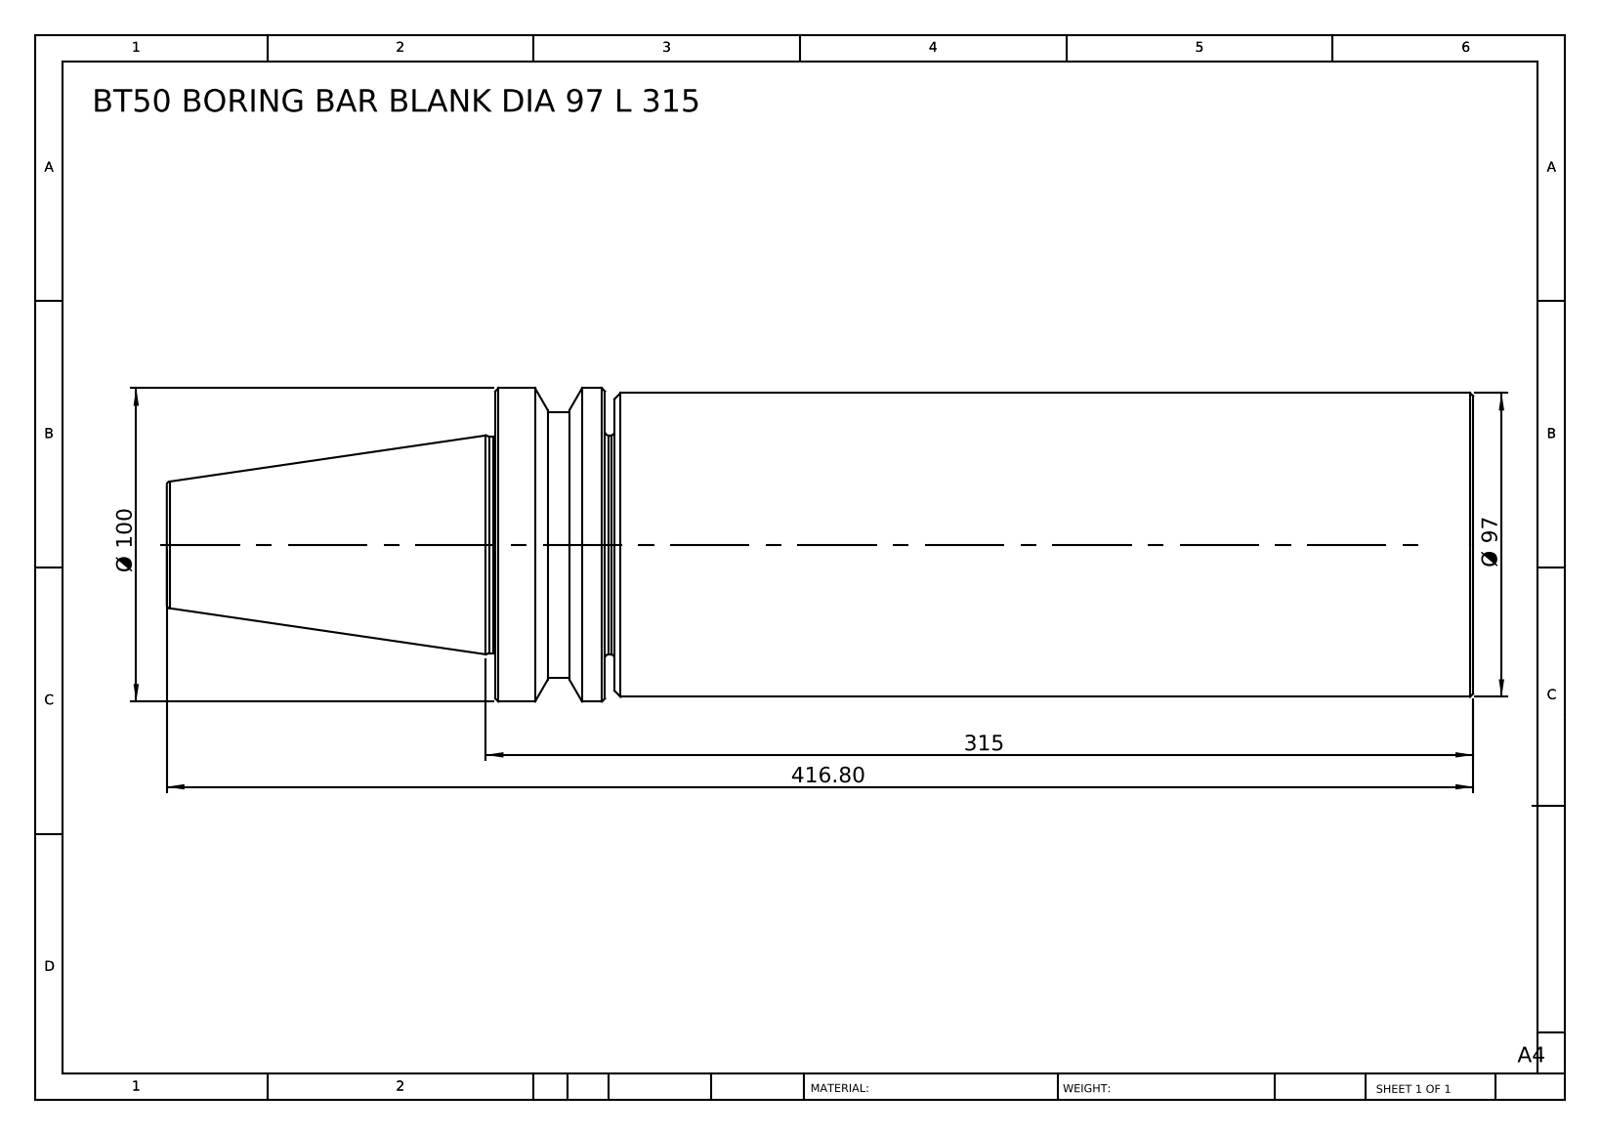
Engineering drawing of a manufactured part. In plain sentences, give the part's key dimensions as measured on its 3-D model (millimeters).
The part is named "BT50 BORING BAR BLANK DIA 97 L 315". Its 3-D file was written by "SolidWorks 2014 (CONFIG_CONTROL_DESIGN)". It is 1 solid with 43 faces: 7 planar, 12 cylindrical and 24 other. Overall it measures 416.8 by 100 by 100 millimeters. Its volume is 2 546 000 cubic millimeters and its surface area 134 873 square millimeters. Round bosses or shafts: 1 of diameter 100, 1 of diameter 97, 1 of diameter 85, 1 of diameter 70, 1 of diameter 69. The main face-to-face distances are 312, 277, 35, 274, 3, 38, 416.8, 142.8, 139.8, 104.8.
